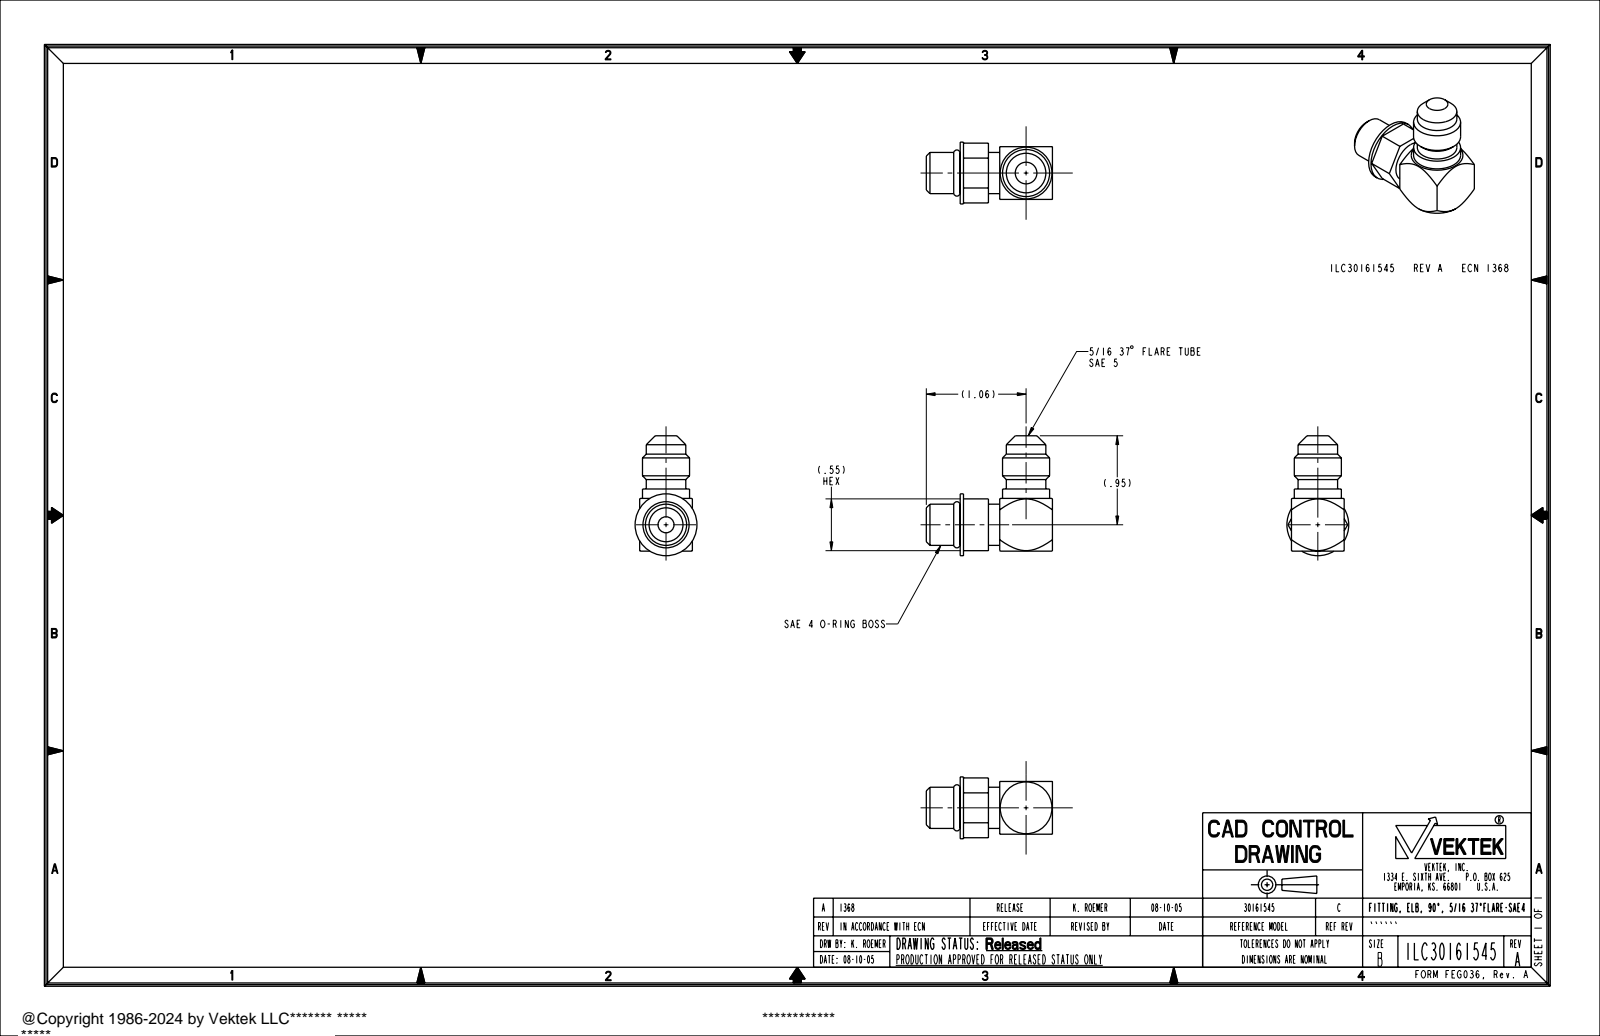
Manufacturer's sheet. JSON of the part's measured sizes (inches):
{"part_name": "ILC30161545", "step_written_by": "PRO/ENGINEER BY PARAMETRIC TECHNOLOGY CORPORATION, 2004290 (AUTOMOTIVE_DESIGN_CC2)", "units": "inches", "bodies": {"solids": 1, "faces": 60, "planar": 22, "cylindrical": 24, "other": 14}, "overall_size": [1.34, 1.274, 0.657], "volume_in3": 0.37, "surface_area_in2": 5.437, "round_holes": [[0.17, 1], [0.23, 1]], "round_bosses_or_shafts": [[0.657, 1], [0.5, 1], [0.437, 1], [0.42, 1]], "face_to_face_distances": [0.56, 0.55, 0.98, 0.66, 0.68, 0.3, 0.12, 0.42, 0.555, 1.34]}
